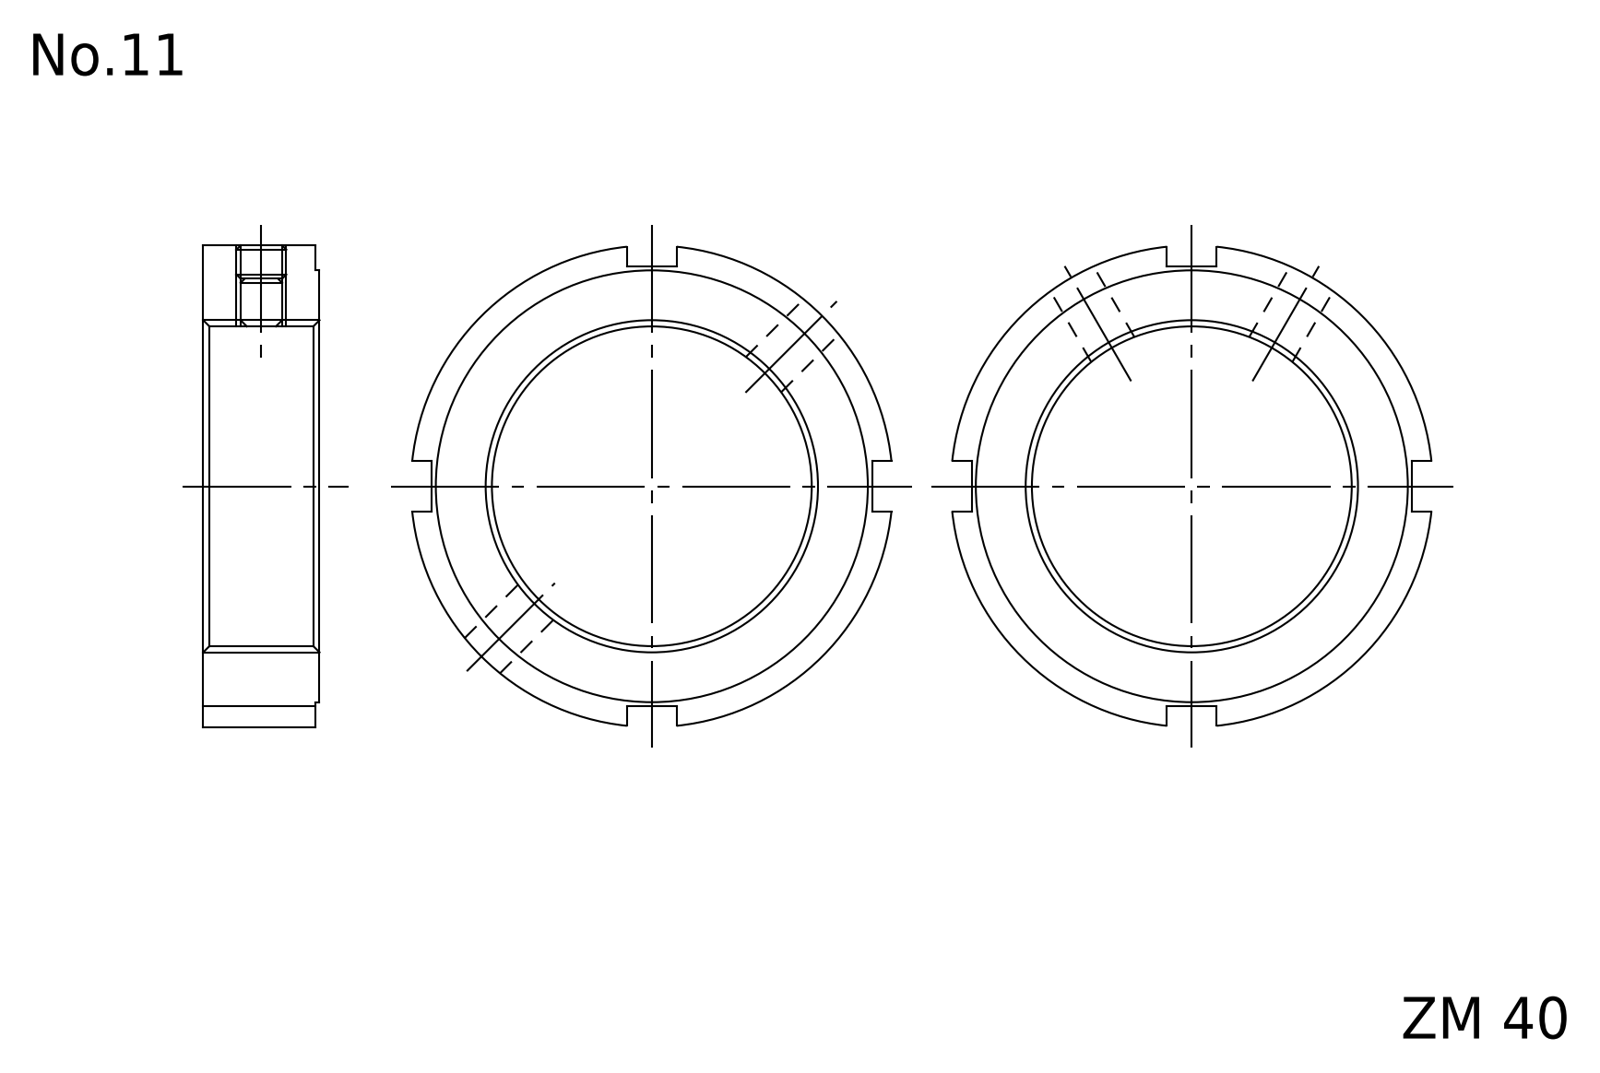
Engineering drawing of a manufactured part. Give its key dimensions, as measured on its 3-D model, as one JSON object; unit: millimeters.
{"part_name": "FKD ZM 40", "step_written_by": "Autodesk Inventor 2011 (AUTOMOTIVE_DESIGN)", "units": "millimeters", "bodies": {"solids": 1, "faces": 23, "planar": 15, "cylindrical": 8, "other": 0}, "overall_size": [57.69, 57.69, 14], "volume_mm3": 18002, "surface_area_mm2": 7410, "round_holes": [[4.92, 2], [40, 1]], "round_bosses_or_shafts": [[58, 1], [52, 1]], "face_to_face_distances": [14, 0.5, 13.5, 23.5, 29.5, 53, 6]}
